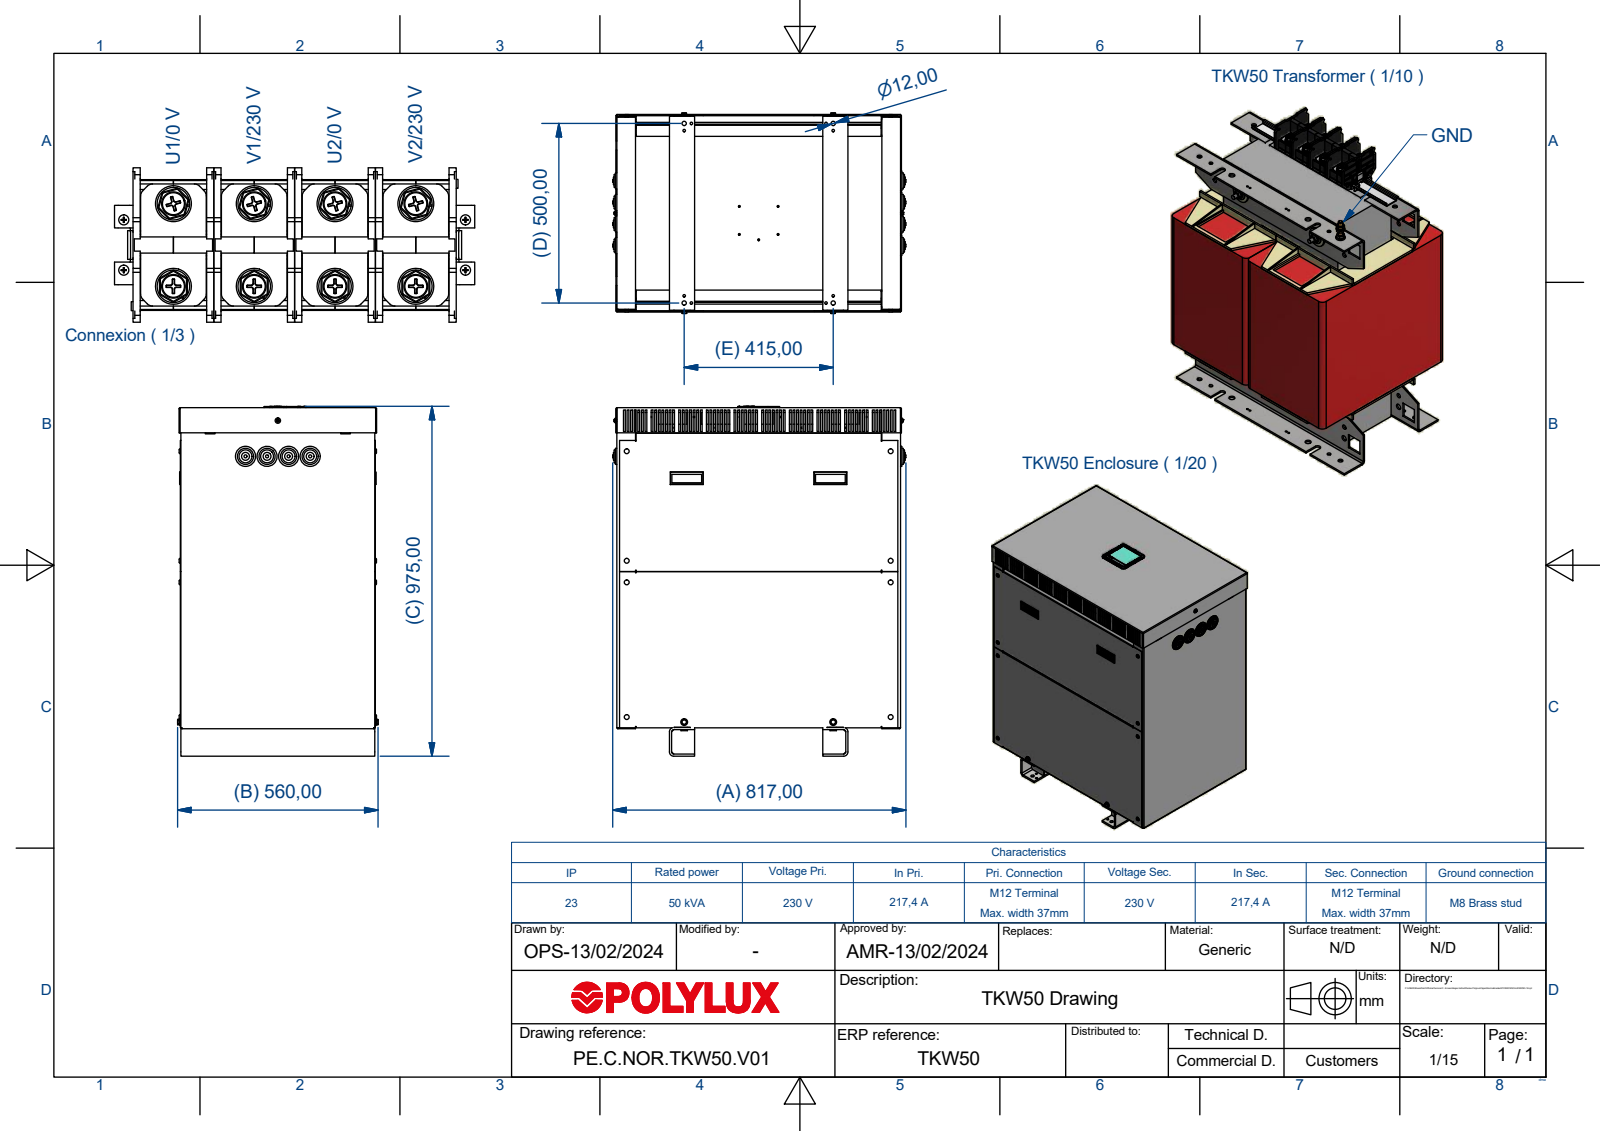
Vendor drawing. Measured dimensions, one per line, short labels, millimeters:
name: CAJ23RC90-1E
written by: Autodesk Inventor 2018 (AUTOMOTIVE_DESIGN)
unit: mm
bodies: 0 solids, 2127 faces (1440 planar, 348 cylindrical, 339 other)
size: 974.09 × 816.48 × 558.2
holes: 16× ⌀11, 8× ⌀7, 6× ⌀4, 4× ⌀12, 4× ⌀48
bosses: 8× ⌀13.59, 4× ⌀56, 4× ⌀45, 4× ⌀36, 4× ⌀22, 4× ⌀11.4, 4× ⌀8.5, 3× ⌀18.8
rounds: 43× R0.2, 32× R0.3, 28× R0.5, 23× R3, 20× R1.5, 5× R0.15, 4× R5.5, 4× R6
face distances: 1.5, 541.5, 788.5, 540, 543, 790, 787, 3, 538.5, 5
hole spacings: 20, 427.47, 60, 40, 428.87, 120, 431.19, 80
